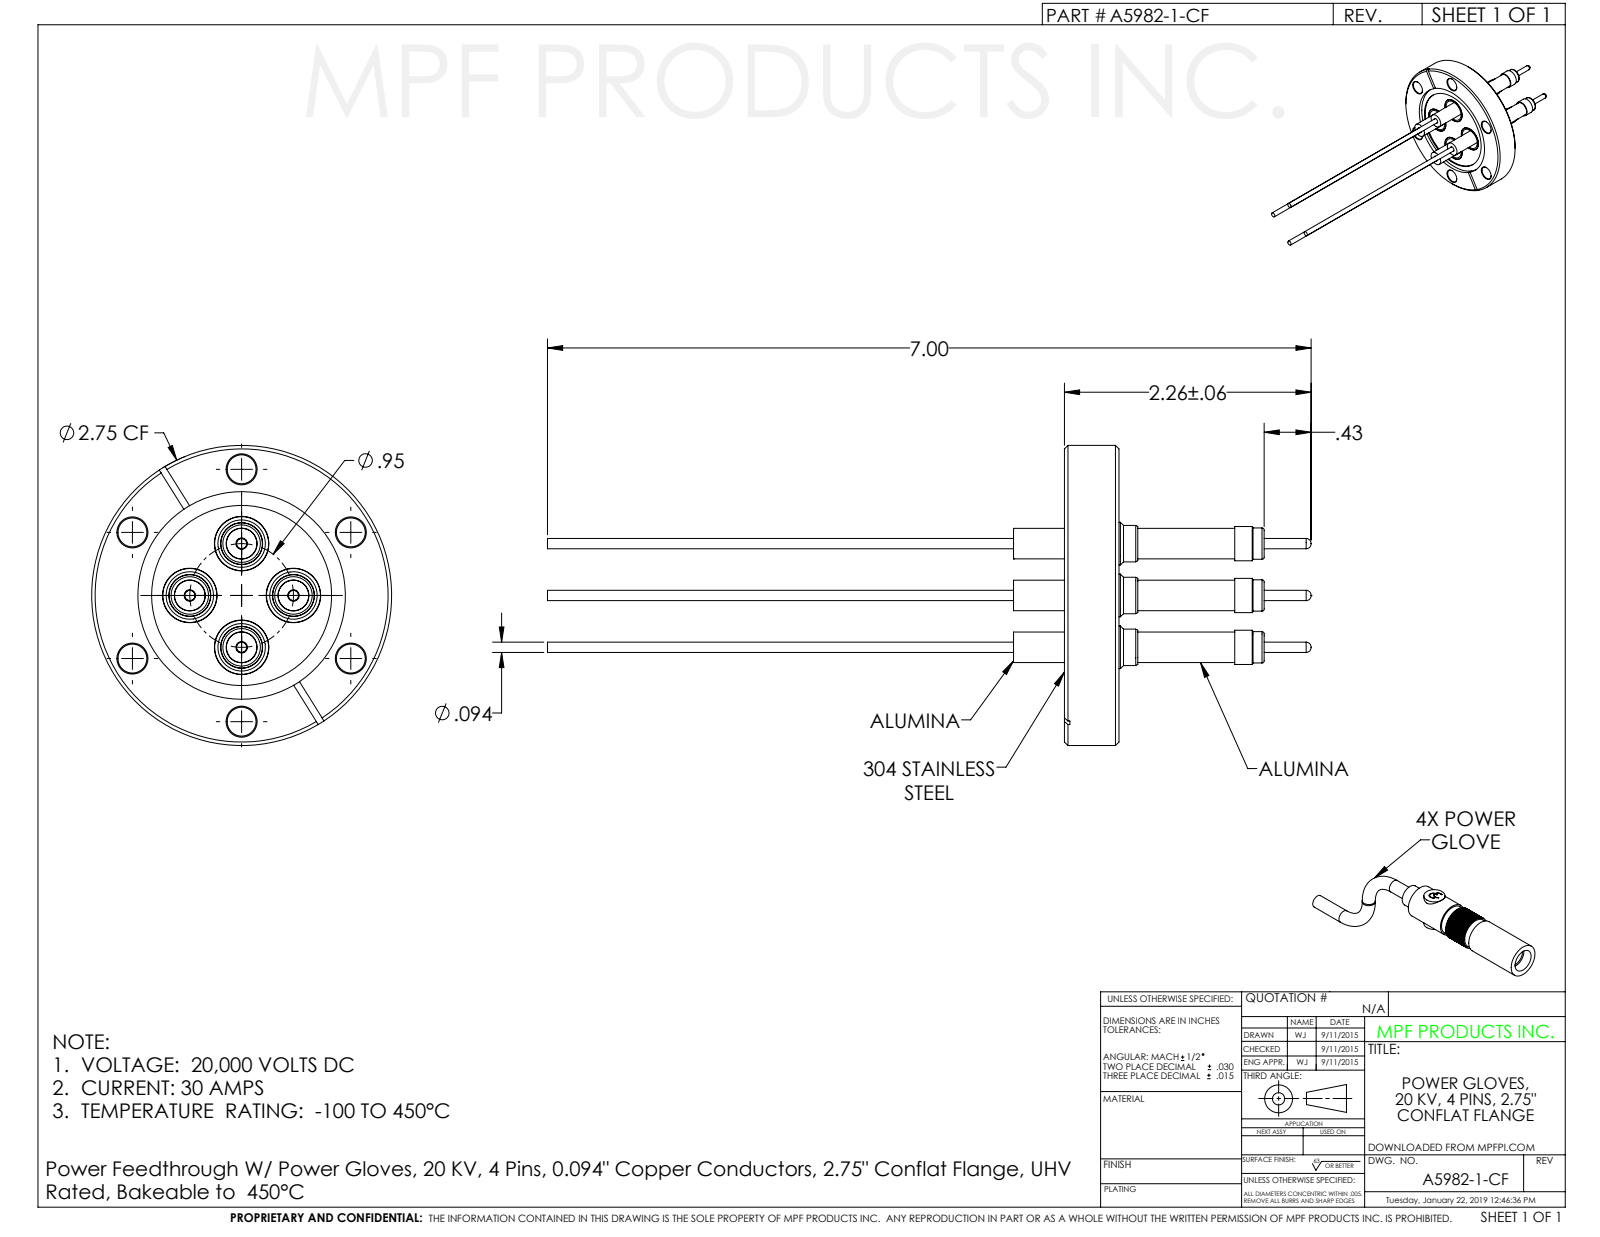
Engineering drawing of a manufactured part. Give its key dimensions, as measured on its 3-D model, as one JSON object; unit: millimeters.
{"part_name": "A5982-1-CF", "step_written_by": "SolidWorks 2012 (CONFIG_CONTROL_DESIGN)", "units": "millimeters", "bodies": {"solids": 1, "faces": 309, "planar": 55, "cylindrical": 140, "other": 114}, "overall_size": [177.8, 69.9, 69.9], "volume_mm3": 51060, "surface_area_mm2": 27260, "round_holes": [[6.7, 6], [2.7, 4], [6.6, 4], [8.7, 4], [9.8, 4], [11, 4], [12.4, 4], [41.9, 1], [48, 1], [48.3, 1]], "round_bosses_or_shafts": [[9.9, 4], [9.4, 4], [7.9, 4], [7.8, 4], [7.3, 4], [7.1, 4], [2.4, 4], [69.9, 1]], "face_to_face_distances": [12.7, 1.2, 11.5, 10.9, 9.7, 1.8, 11.7, 12.8, 22.6, 24.4], "hole_center_spacings": [12.1, 17.1, 29.5, 51, 58.9, 19.9, 20, 24.1]}
